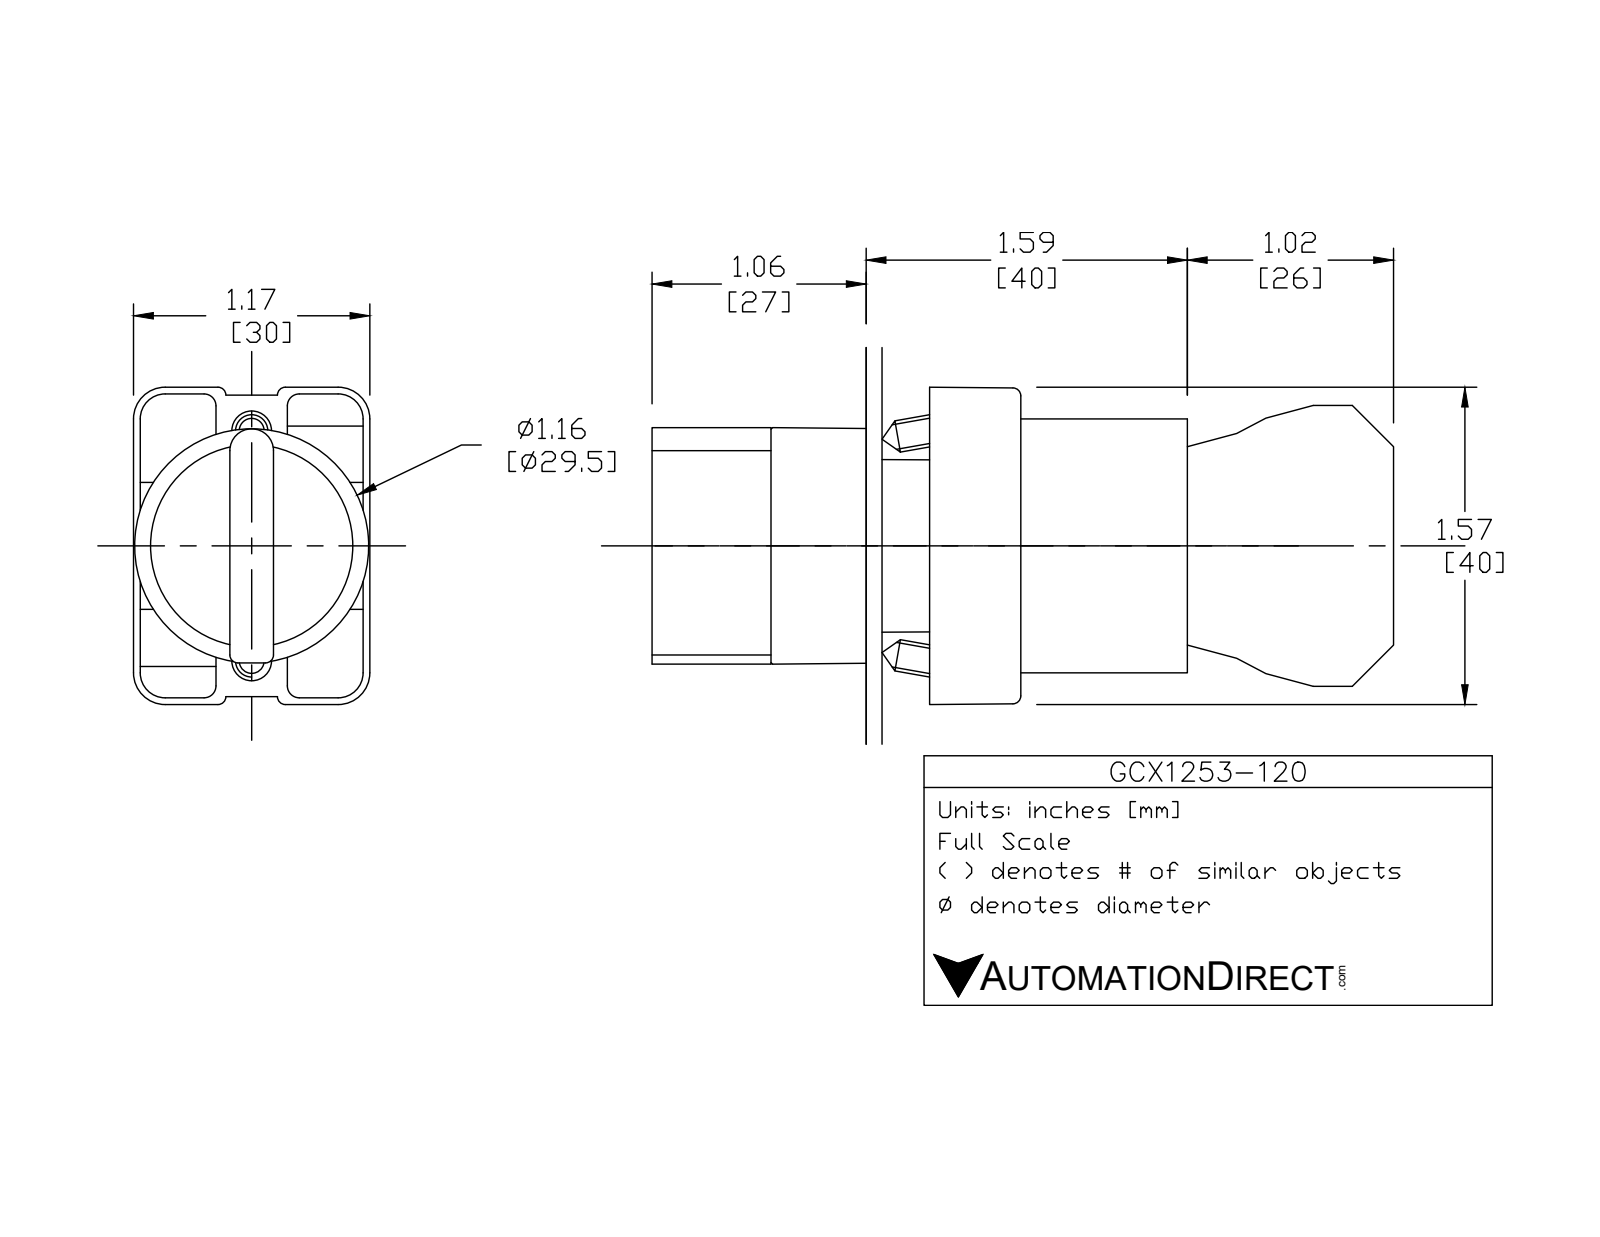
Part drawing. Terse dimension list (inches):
name: GCX1253 OPERATOR; ECX1050; ecx1040; ecx1029 (+1 more)
written by: SolidWorks 2016 (AUTOMOTIVE_DESIGN)
unit: in
bodies: 8 solids, 445 faces (263 planar, 151 cylindrical, 31 other)
size: 3.653 × 1.581 × 1.177
volume: 2.799 in³; area: 39 in²
holes: 2× ⌀0.079, 2× ⌀0.124, 2× ⌀0.13, 1× ⌀0.087, 1× ⌀0.197, 1× ⌀0.469, 1× ⌀0.878, 1× ⌀0.888, 1× ⌀1.024
bosses: 4× ⌀0.157, 1× ⌀1.175, 1× ⌀1.004, 1× ⌀0.945, 1× ⌀0.856, 1× ⌀0.78, 1× ⌀0.504
rounds: 24× R0.059, 12× R0.041, 12× R0.124, 12× R0.157, 9× R0.039, 2× R0.128, 1× R0.02, 1× R0.063
face distances: 0.827, 2.02, 1.193, 0.579, 1.244, 1.171, 0.472, 0.469, 0.031, 0.033
hole spacings: 0.236, 0.544, 0.472, 0.49
